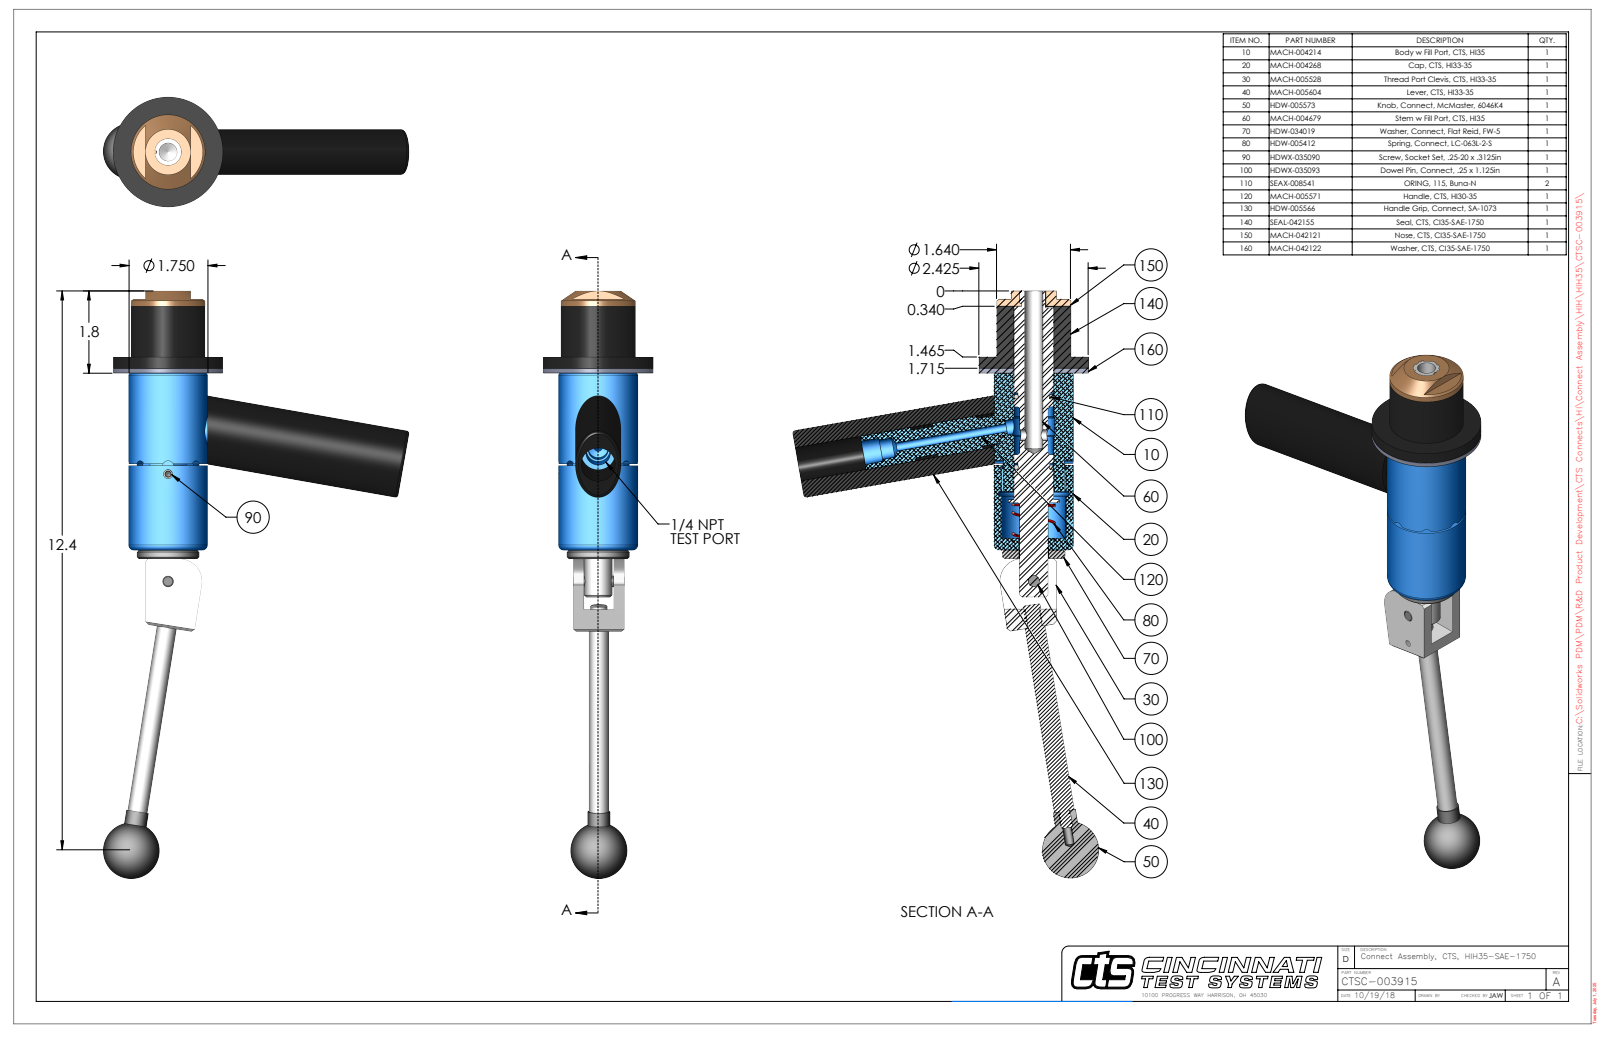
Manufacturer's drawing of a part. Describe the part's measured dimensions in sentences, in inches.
The part is named "CTSC-003915". Its 3-D file was written by "SolidWorks 2023 (AUTOMOTIVE_DESIGN)". It is 10 solids with 302 faces: 107 planar, 127 cylindrical and 68 other. Overall it measures 13.02 by 6.763 by 2.425 inches. Its volume is 21.09 cubic inches and its surface area 141.4 square inches. Round holes: 2 of diameter 0.201, 1 of diameter 0.15, 1 of diameter 0.187, 1 of diameter 0.249, 1 of diameter 0.25, 1 of diameter 0.251, 1 of diameter 0.313, 1 of diameter 0.406, 1 of diameter 0.438, 1 of diameter 0.531, 1 of diameter 0.635, 1 of diameter 0.656. Round bosses or shafts: 2 of diameter 0.25, 1 of diameter 2.425, 1 of diameter 1.75, 1 of diameter 1.64, 1 of diameter 1.38, 1 of diameter 0.869, 1 of diameter 0.75, 1 of diameter 0.625. Partial cylindrical surfaces (rounded edges, fillets, slot ends): 4 of radius 0.125, 2 of radius 0.029, 1 of radius 0.166, 1 of radius 0.166, 1 of radius 0.248, 1 of radius 0.33, 1 of radius 0.5, 1 of radius 0.695. The main face-to-face distances are 0.11, 1.375, 1.485, 0.25, 1.125, 0.36, 5.405, 4.28, 4.03, 3.92. The hole center spacings are 0.74, 2.376, 3.116.
